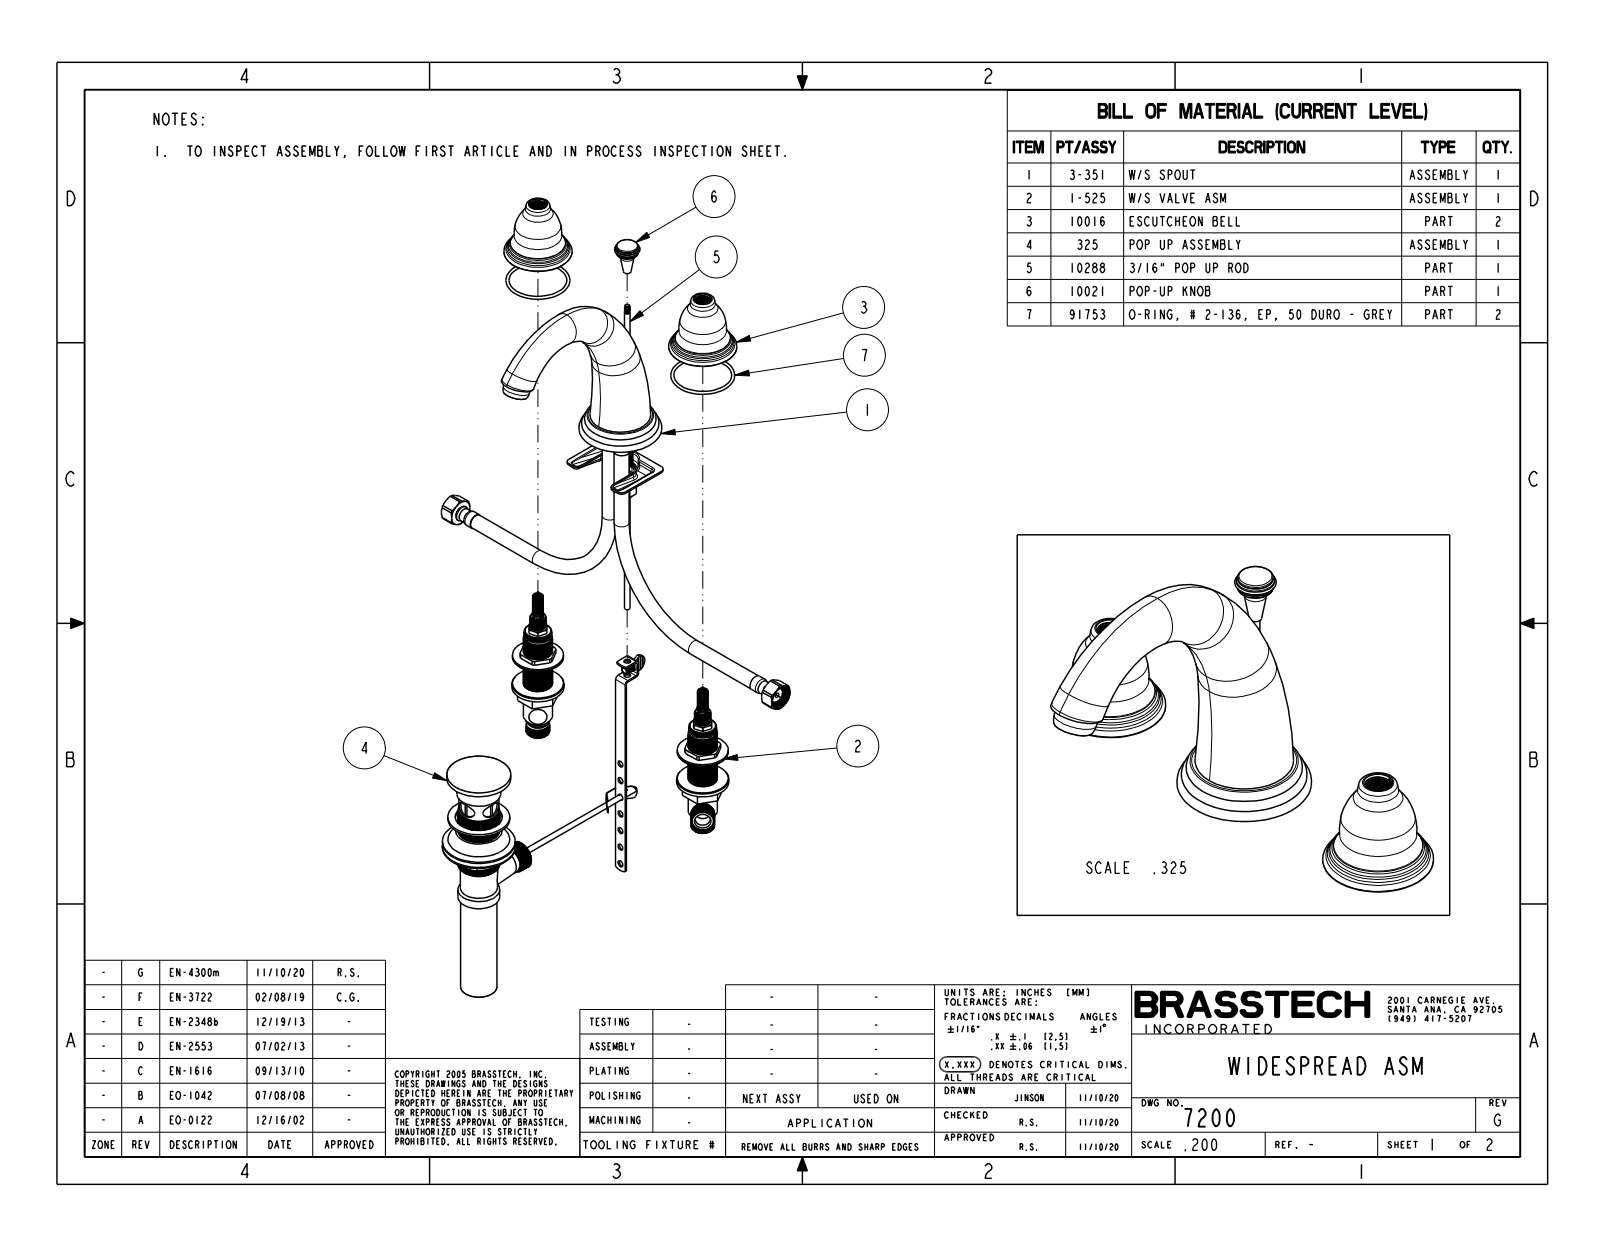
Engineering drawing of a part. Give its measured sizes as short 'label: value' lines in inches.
name: 7200
written by: CREO PARAMETRIC BY PTC INC, 2018400 (CONFIG_CONTROL_DESIGN)
unit: in
bodies: 3 solids, 165 faces (15 planar, 31 cylindrical, 119 other)
size: 10.34 × 6.957 × 6.08
volume: 26.12 in³; area: 88.37 in²
holes: 1× ⌀0.15, 1× ⌀0.195, 1× ⌀0.21
bosses: 2× ⌀2.34, 1× ⌀0.925, 1× ⌀0.88, 1× ⌀0.812, 1× ⌀0.746, 1× ⌀0.187, 1× ⌀0.14
face distances: 2.008, 0.575, 1.433, 0.359, 0.355, 4.1, 3.525, 2.092, 4.5, 3.925
